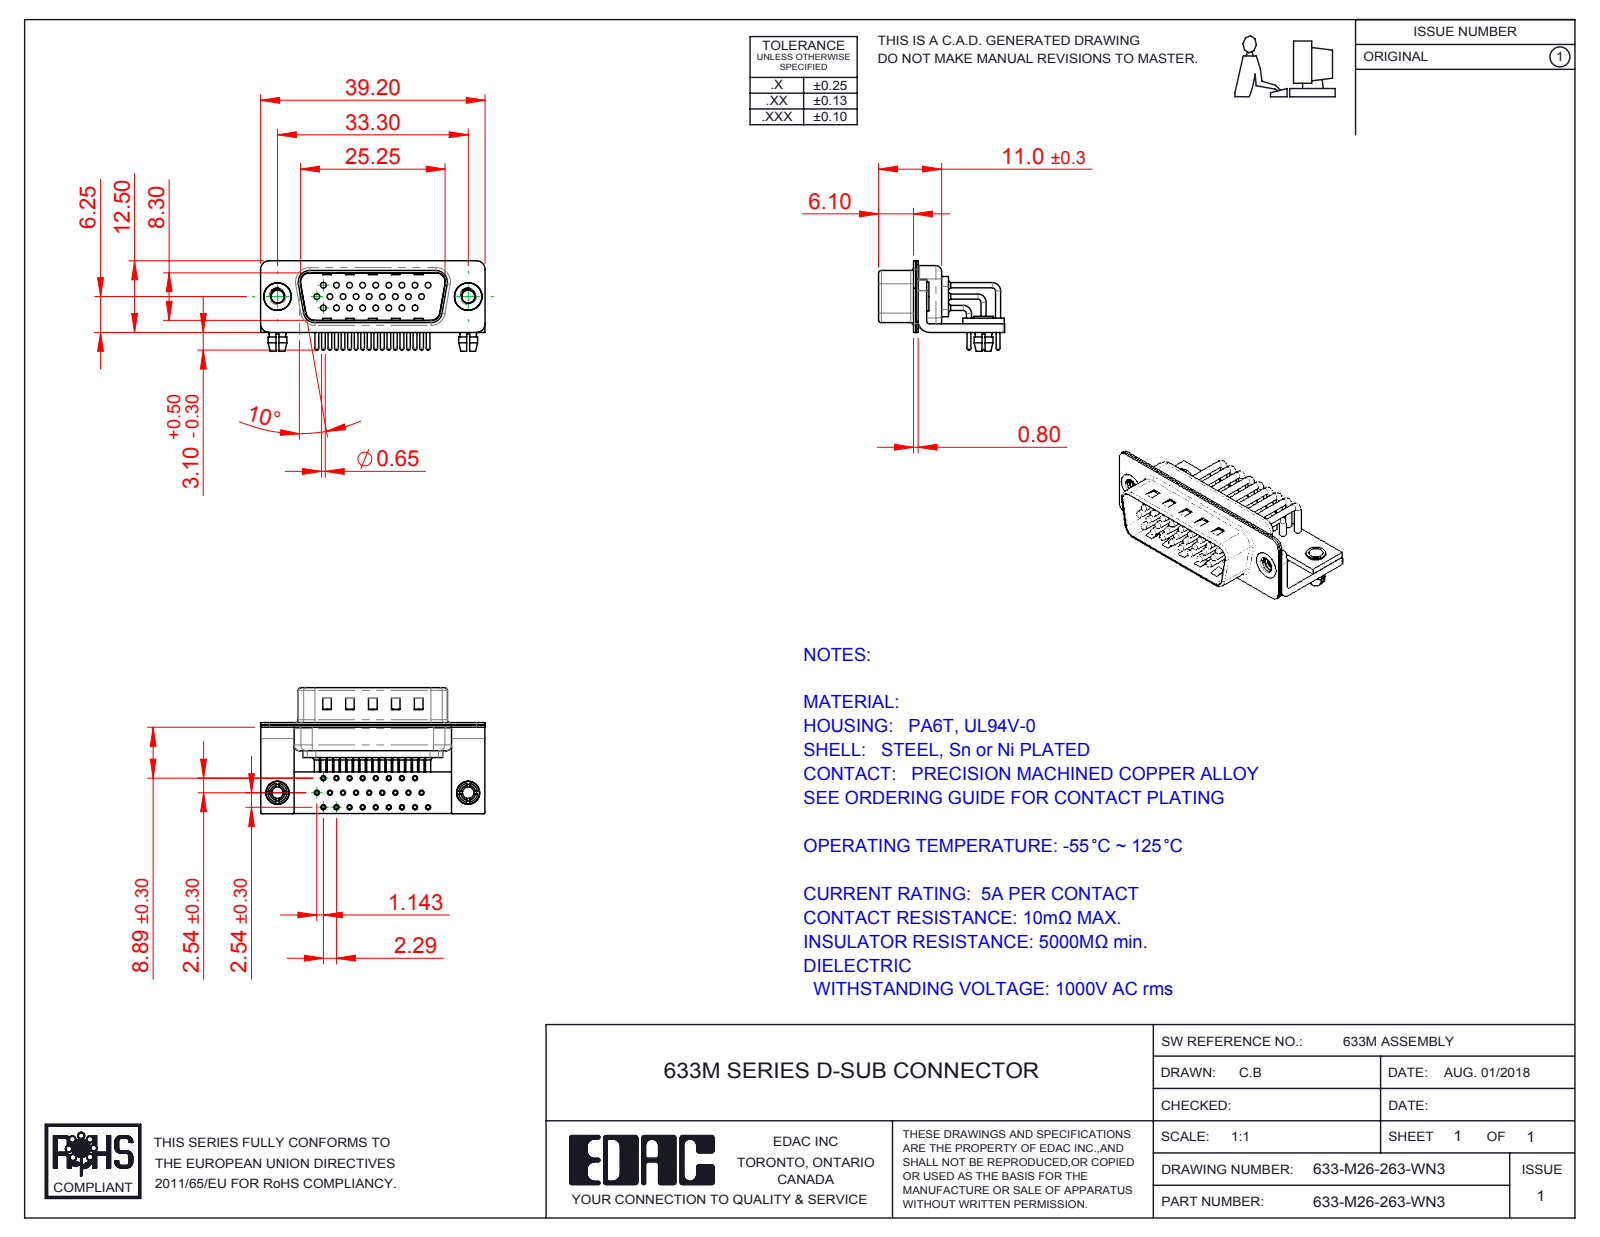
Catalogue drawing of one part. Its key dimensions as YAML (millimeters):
part_name: "633M Contact Row 1; 633M Shell Rear_26 Contacts; 633M Stabilizer Bracket; 633M 4-40 Threaded Rivet_Stabilizer (+7 more)"
step_written_by: "SolidWorks 2016 (CONFIG_CONTROL_DESIGN)"
units: millimeters
bodies: {solids: 36, faces: 3394, planar: 1877, cylindrical: 1175, other: 342}
overall_size: [39.2, 22, 15.8]
volume: 2666
surface_area: 8233
round_holes:
  - {diameter: 2, count: 28}
  - {diameter: 0.9, count: 26}
  - {diameter: 1, count: 26}
  - {diameter: 1.7, count: 26}
  - {diameter: 2.26, count: 2}
  - {diameter: 2.5, count: 2}
  - {diameter: 3.2, count: 2}
  - {diameter: 4, count: 2}
  - {diameter: 4.8, count: 2}
round_bosses_or_shafts:
  - {diameter: 1.5, count: 26}
  - {diameter: 0.9, count: 26}
  - {diameter: 0.65, count: 26}
  - {diameter: 5, count: 2}
  - {diameter: 4.9, count: 2}
  - {diameter: 4, count: 2}
  - {diameter: 3.4, count: 2}
  - {diameter: 3.3, count: 2}
partial_cylinders:
  - {radius: 1.01, count: 26}
  - {radius: 0.25, count: 16}
  - {radius: 1.5, count: 16}
  - {radius: 2, count: 13}
  - {radius: 0.5, count: 9}
  - {radius: 1.6, count: 8}
  - {radius: 0.6, count: 4}
  - {radius: 0.65, count: 4}
face_to_face_distances: [0.4, 1.5, 0.85, 0.8, 1, 1.25, 1.9, 10.4, 9.55, 2.5]
hole_center_spacings: [4.57, 2.29, 2.28, 3.96, 6.86, 4.27, 6.05, 2.78]
